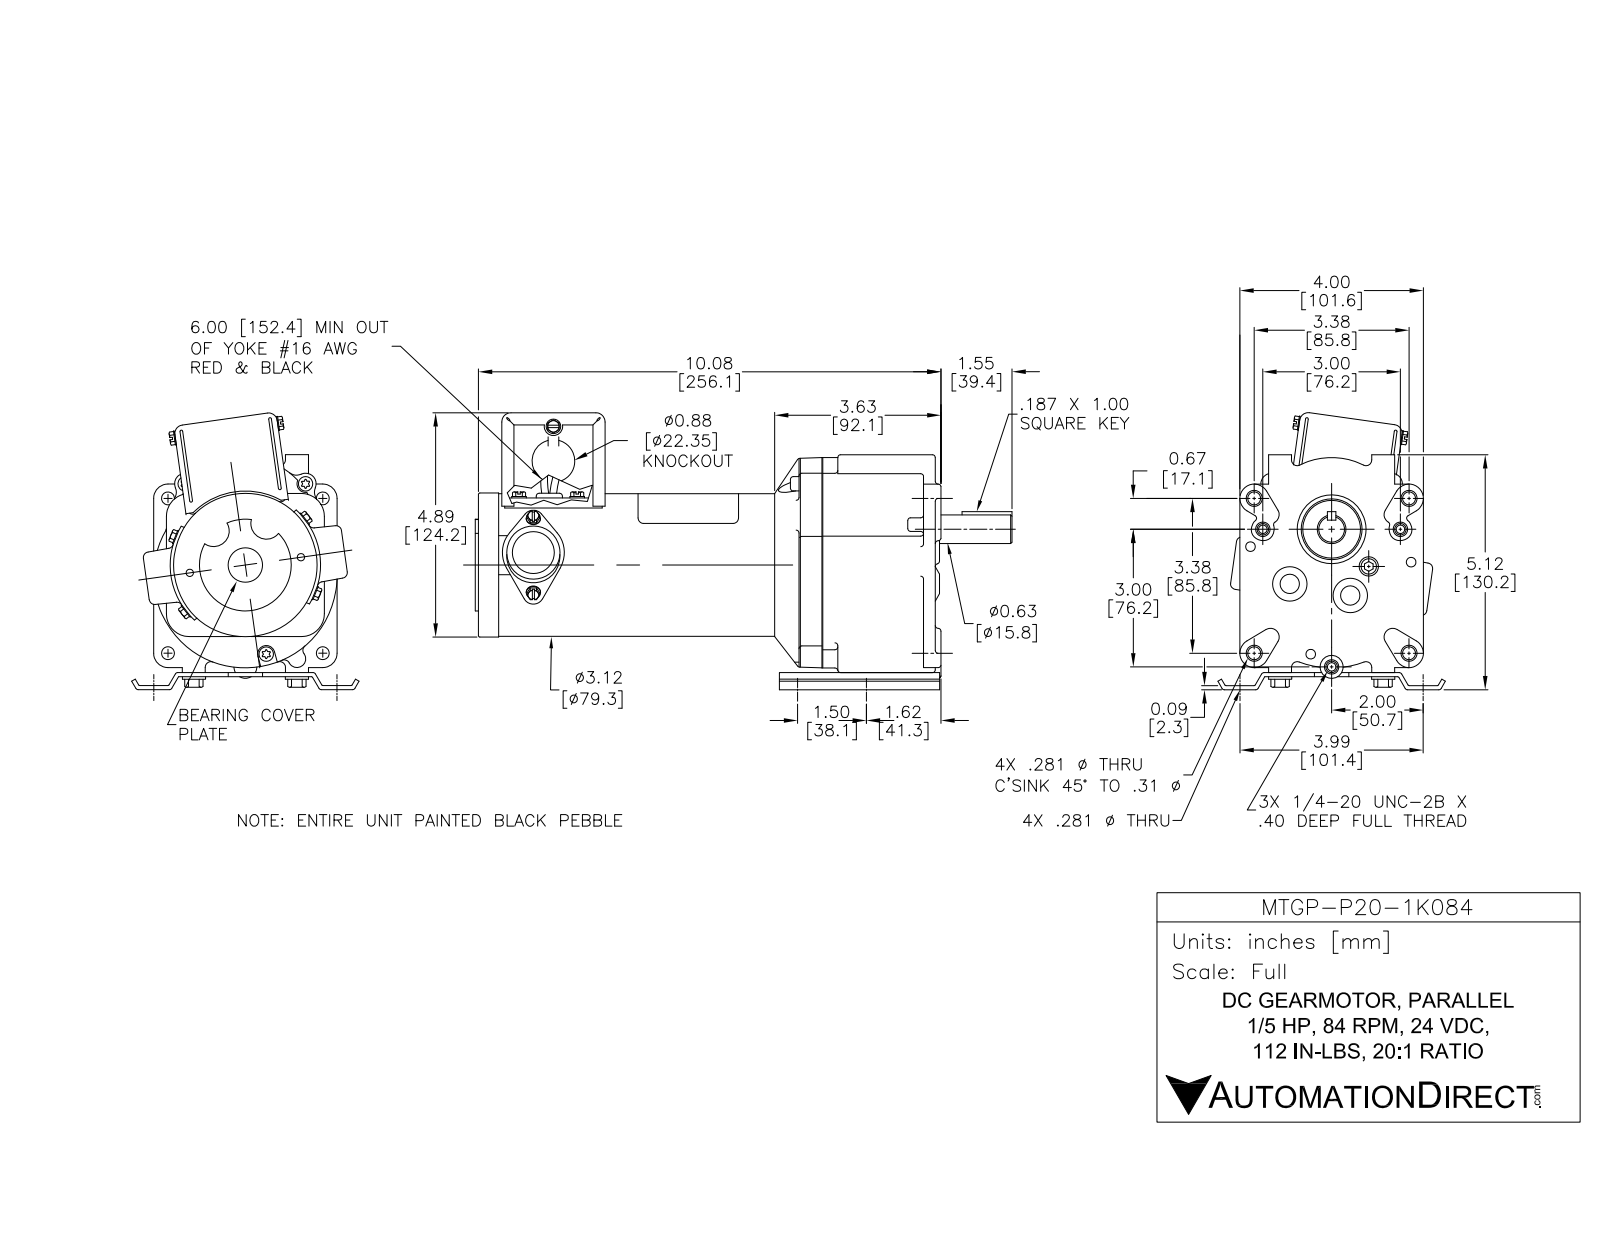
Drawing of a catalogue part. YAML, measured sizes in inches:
part_name: "MTGP-P20-1K084"
step_written_by: "SolidWorks 2014 (AUTOMOTIVE_DESIGN)"
units: inches
bodies: {solids: 53, faces: 984, planar: 567, cylindrical: 365, other: 52}
overall_size: [11.698, 6.209, 4.939]
volume: 65.11
surface_area: 470.6
round_holes:
  - {diameter: 0.3, count: 11}
  - {diameter: 0.5, count: 5}
  - {diameter: 0.25, count: 4}
  - {diameter: 0.345, count: 4}
  - {diameter: 0.21, count: 3}
  - {diameter: 0.125, count: 2}
  - {diameter: 0.198, count: 2}
  - {diameter: 0.208, count: 2}
  - {diameter: 0.345, count: 2}
  - {diameter: 0.375, count: 1}
  - {diameter: 0.46, count: 1}
  - {diameter: 0.625, count: 1}
round_bosses_or_shafts:
  - {diameter: 0.314, count: 5}
  - {diameter: 0.3, count: 4}
  - {diameter: 0.208, count: 3}
  - {diameter: 0.46, count: 2}
  - {diameter: 0.1, count: 2}
  - {diameter: 3.156, count: 1}
  - {diameter: 1.325, count: 1}
  - {diameter: 0.625, count: 1}
partial_cylinders:
  - {radius: 0.019, count: 28}
  - {radius: 0.1, count: 23}
  - {radius: 0.025, count: 8}
  - {radius: 0.25, count: 7}
  - {radius: 0.159, count: 4}
  - {radius: 0.19, count: 4}
  - {radius: 0.191, count: 4}
  - {radius: 0.234, count: 4}
face_to_face_distances: [1.375, 3.495, 2.12, 0.09, 0.031, 0.25, 0.063, 0.05, 1.425, 3.545]
hole_center_spacings: [1.62, 1.23, 1.5, 1.504, 1.603, 2.974, 3.375, 6.911]
